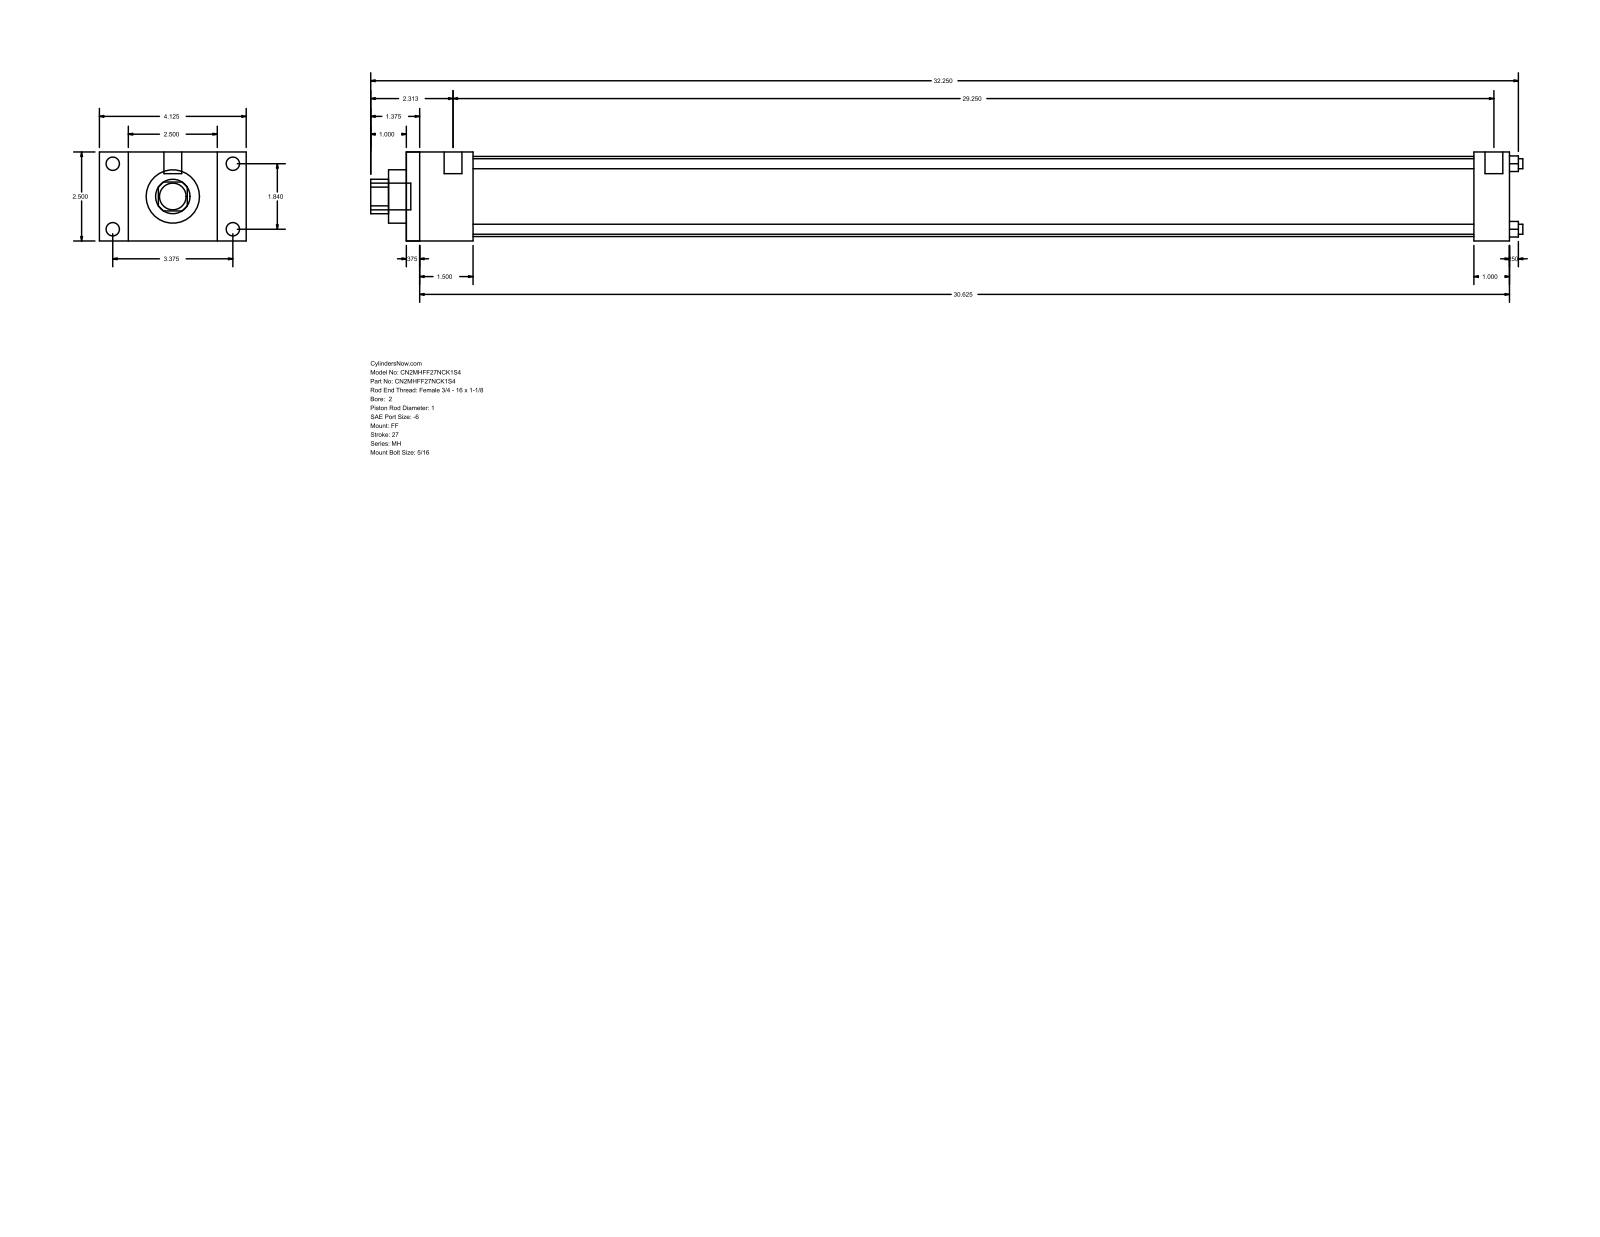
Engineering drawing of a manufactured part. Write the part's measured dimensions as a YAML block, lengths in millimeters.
part_name: "MH_FF__0200_1"
step_written_by: "GSSL Pune (CONFIG_CONTROL_DESIGN)"
units: millimeters
bodies: {solids: 0, faces: 92, planar: 64, cylindrical: 28, other: 0}
overall_size: [822.33, 104.78, 63.5]
round_holes:
  - {diameter: 7.14, count: 4}
  - {diameter: 25.4, count: 1}
  - {diameter: 38.1, count: 1}
  - {diameter: 57.15, count: 1}
round_bosses_or_shafts:
  - {diameter: 9.53, count: 4}
  - {diameter: 5.56, count: 4}
  - {diameter: 12.7, count: 2}
  - {diameter: 19.05, count: 1}
partial_cylinders:
  - {radius: 12.29, count: 1}
face_to_face_distances: [63.5, 787.4, 9.52, 777.88, 20.64, 25.4, 47.63, 762, 38.11, 752.48]
hole_center_spacings: [33.05, 46.74, 66.1]
